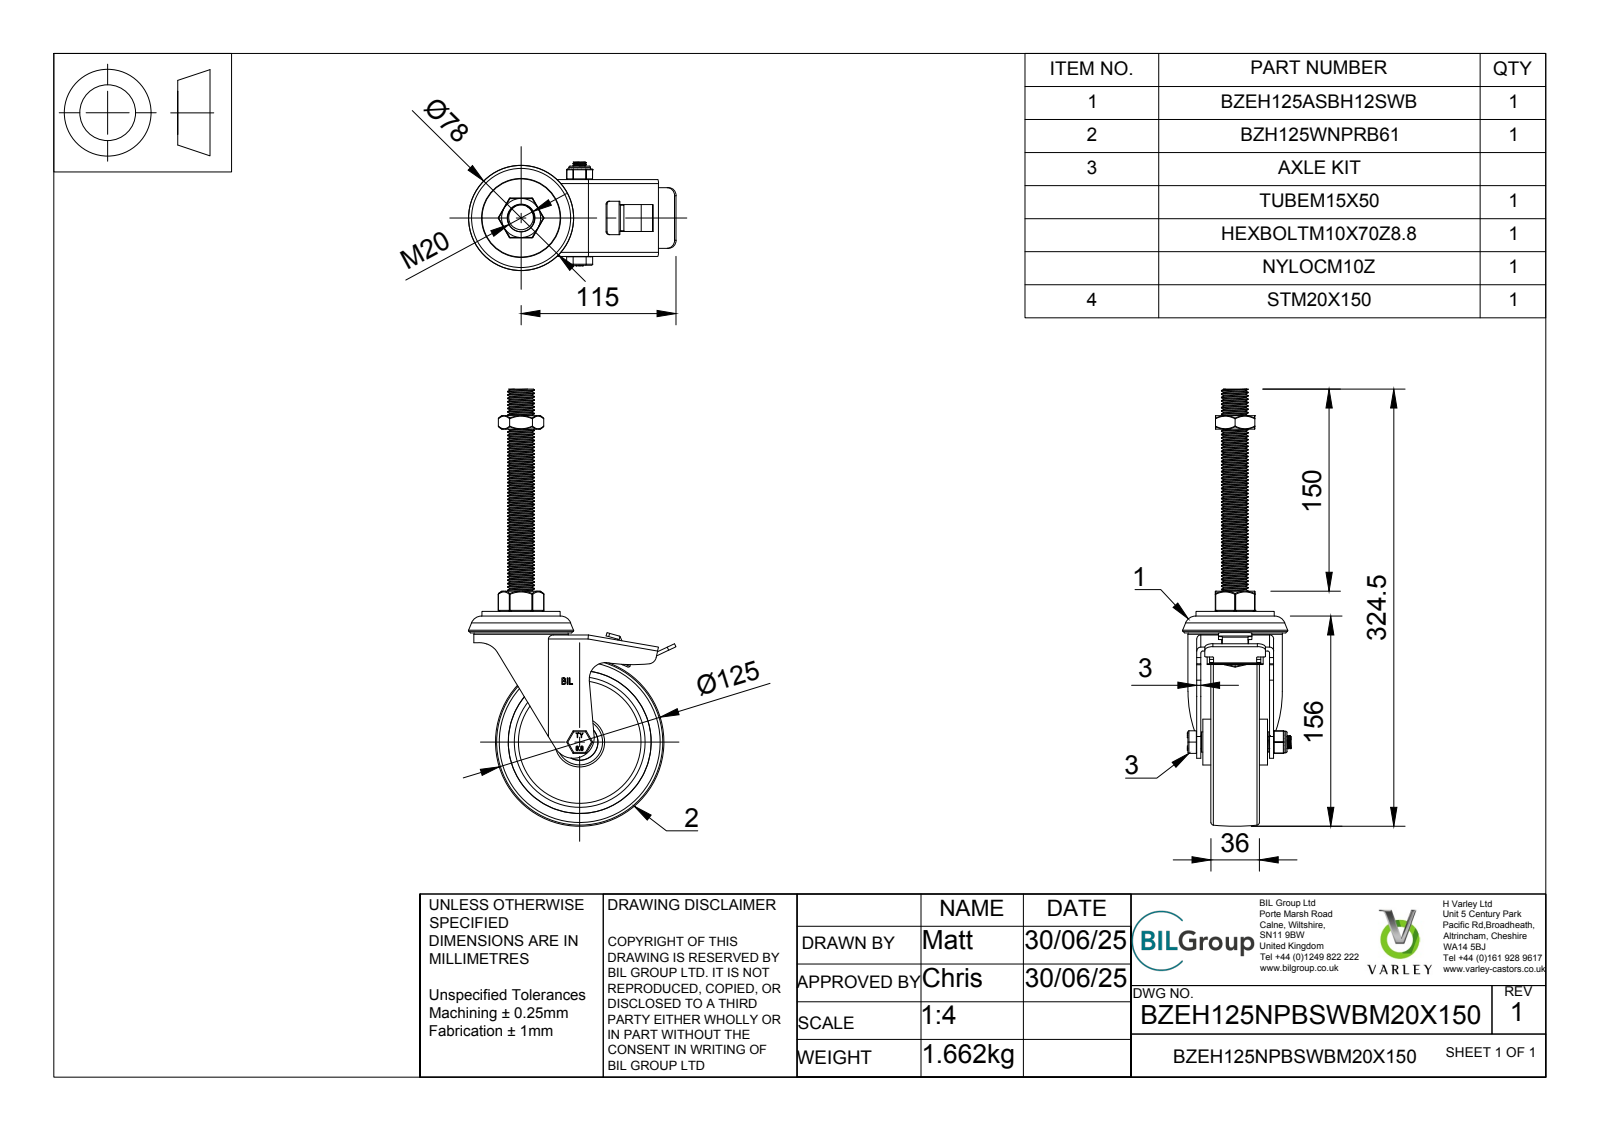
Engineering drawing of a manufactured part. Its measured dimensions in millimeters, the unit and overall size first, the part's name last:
Units: millimetres
Overall size (bounding box): 324.5 × 154 × 80.5
Round holes (diameter × count): ⌀8 ×1, ⌀10 ×1, ⌀10.25 ×1, ⌀10.5 ×1, ⌀12 ×1, ⌀12.2 ×1, ⌀13 ×1, ⌀14.5 ×1, ⌀15.2 ×1, ⌀15.5 ×1, ⌀20 ×1, ⌀21 ×1
Round bosses / shafts (diameter × count): ⌀4 ×9, ⌀16 ×2, ⌀70 ×1, ⌀58 ×1, ⌀53.5 ×1, ⌀34 ×1, ⌀28.75 ×1, ⌀27 ×1
Partial cylindrical surfaces — rounded edges, fillets, slot ends (radius × count): R0.75 ×36, R0.5 ×18, R1 ×11, R1.5 ×9, R3 ×4, R6 ×3, R1.76 ×2, R2 ×2
Main face-to-face distances: 3, 15, 10.5, 21, 6, 22.5, 25.5, 46.5, 7.5, 31.5
Volume: 409 187 mm³ · Surface area: 197 316 mm²
Bodies: 29 solids, 944 faces (371 planar, 392 cylindrical, 181 other)
Part name (STEP PRODUCT): BZEH125NPBSWBM20X150 v3; BZEH125ASBH12SWB v1; ZINC PLATED, PRESSED STEEL TOP HEAD; ZINC PLATED, PRESSED STEEL FORKS (+8 more)
STEP written by: Autodesk Translation Framework v14.10.0.0 (AUTOMOTIVE_DESIGN)
